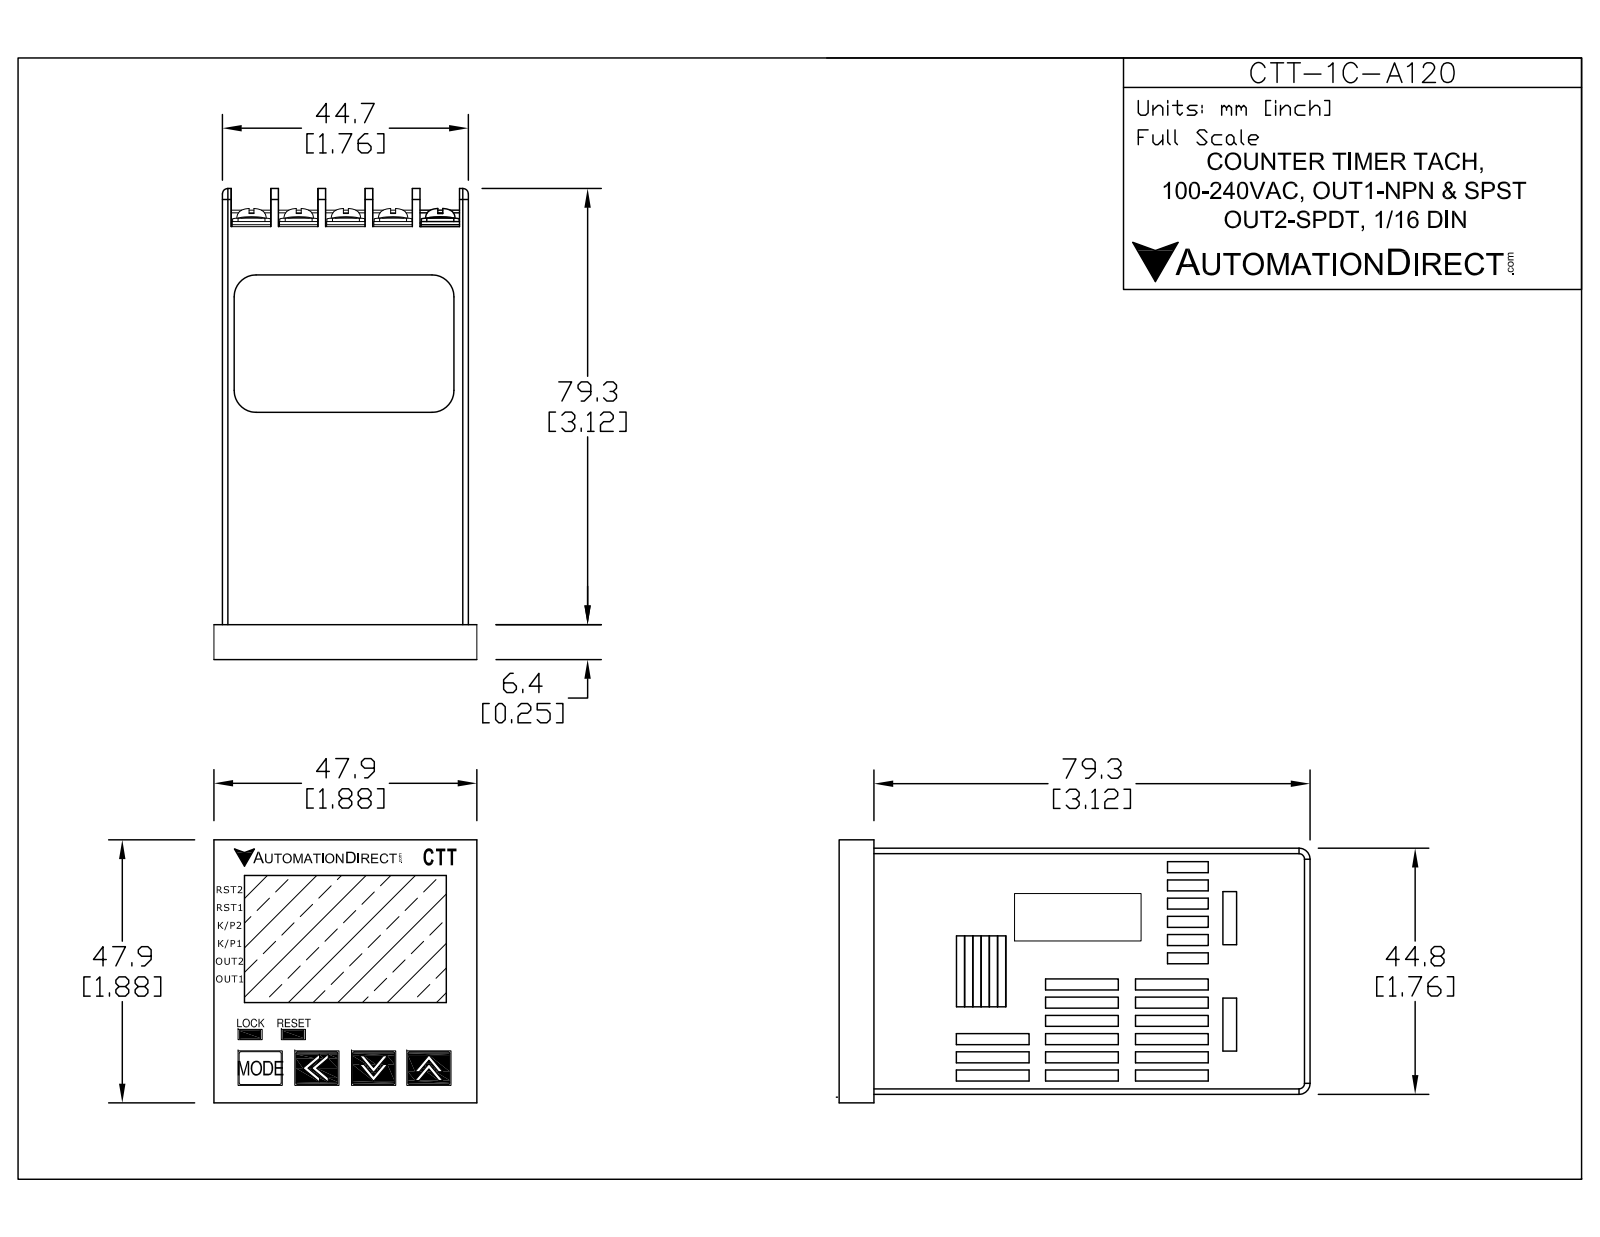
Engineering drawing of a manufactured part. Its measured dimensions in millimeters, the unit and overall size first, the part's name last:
Units: millimetres
Overall size (bounding box): 86.7 × 56.4 × 48
Round holes (diameter × count): ⌀3 ×2
Round bosses / shafts (diameter × count): ⌀5.3 ×15, ⌀5.3 ×2, ⌀2.9 ×2
Partial cylindrical surfaces — rounded edges, fillets, slot ends (radius × count): R0.3 ×92, R0.3 ×16, R0.2 ×8, R1 ×6, R1.1 ×4, R0.8 ×2, R3 ×2, R4 ×2
Main face-to-face distances: 44.8, 8.6, 1.2, 46.1, 17.2, 7.2, 15.8, 1.4, 47.3, 1.5
Hole centre spacings: 63.7
Volume: 169 900 mm³ · Surface area: 33 810 mm²
Bodies: 4 solids, 1082 faces (701 planar, 240 cylindrical, 141 other)
Part name (STEP PRODUCT): CTT-1C-A120
STEP written by: SolidWorks 2017 (AUTOMOTIVE_DESIGN)
